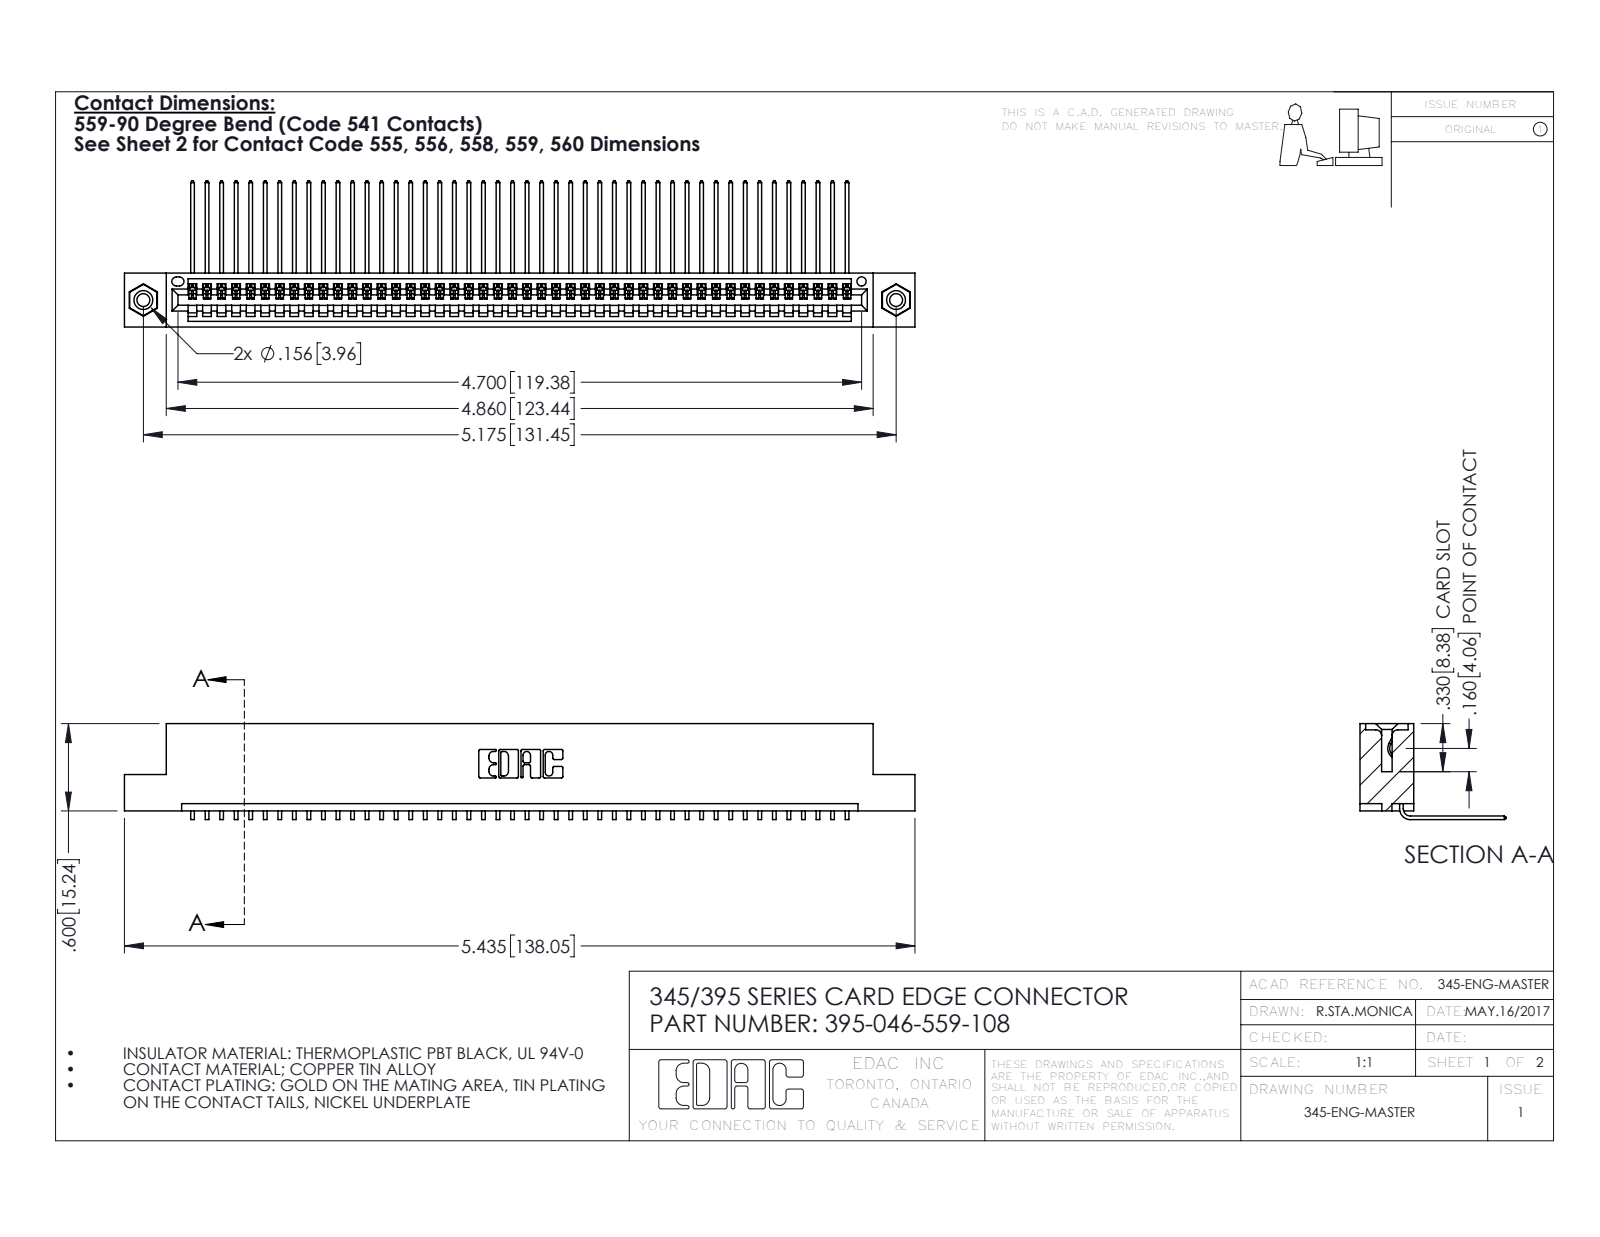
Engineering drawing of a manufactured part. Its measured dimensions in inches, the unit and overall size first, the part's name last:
Units: inches
Overall size (bounding box): 5.435 × 1.005 × 0.659
Round holes (diameter × count): ⌀0.089 ×2, ⌀0.125 ×2, ⌀0.156 ×2, ⌀0.064 ×1
Round bosses / shafts (diameter × count): ⌀0.155 ×2
Partial cylindrical surfaces — rounded edges, fillets, slot ends (radius × count): R0.006 ×92, R0.01 ×22, R0.007 ×6, R0.031 ×6, R0.026 ×3, R0.031 ×2, R0.04 ×2, R0.014 ×1
Main face-to-face distances: 0.072, 0.298, 0.37, 0.2, 0.098, 0.272, 0.025, 0.225, 0.149, 0.072
Hole centre spacings: 0.27, 4.939, 5.175
Volume: 0.811 in³ · Surface area: 28.89 in²
Bodies: 49 solids, 2946 faces (2044 planar, 886 cylindrical, 16 other)
Part name (STEP PRODUCT): 395-046-559-108; 345-292-001_558 559 Tail - 1; 345-250-001_345-250-003-102; 345 Part_Flush Mounting Lugs - 0.156 Dia-TI
STEP written by: SolidWorks 2016 (CONFIG_CONTROL_DESIGN)
